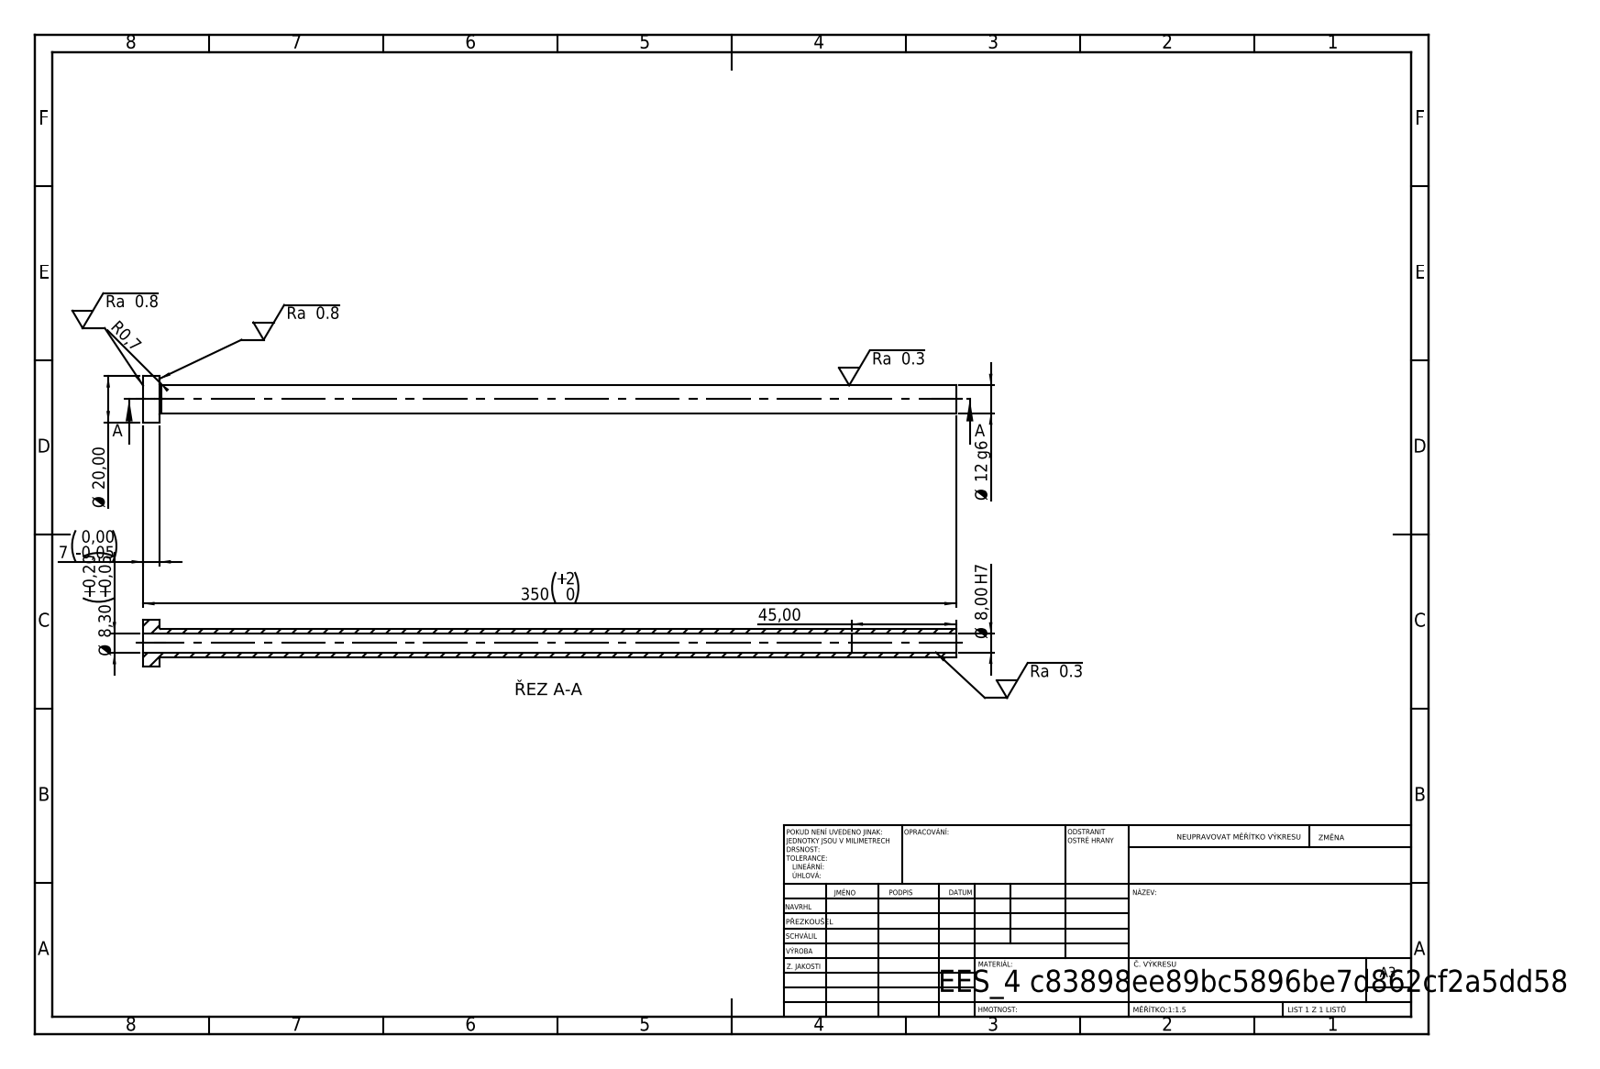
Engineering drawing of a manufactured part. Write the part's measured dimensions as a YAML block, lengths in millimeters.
step_written_by: "SolidWorks 2019 (CONFIG_CONTROL_DESIGN)"
units: millimeters
bodies: {solids: 1, faces: 14, planar: 4, cylindrical: 8, other: 2}
overall_size: [350, 20, 20]
volume: 22231
surface_area: 22971
round_holes:
  - {diameter: 8, count: 1}
  - {diameter: 8.3, count: 1}
round_bosses_or_shafts:
  - {diameter: 20, count: 1}
  - {diameter: 12, count: 1}
face_to_face_distances: [7, 350, 343, 305, 298, 45]
